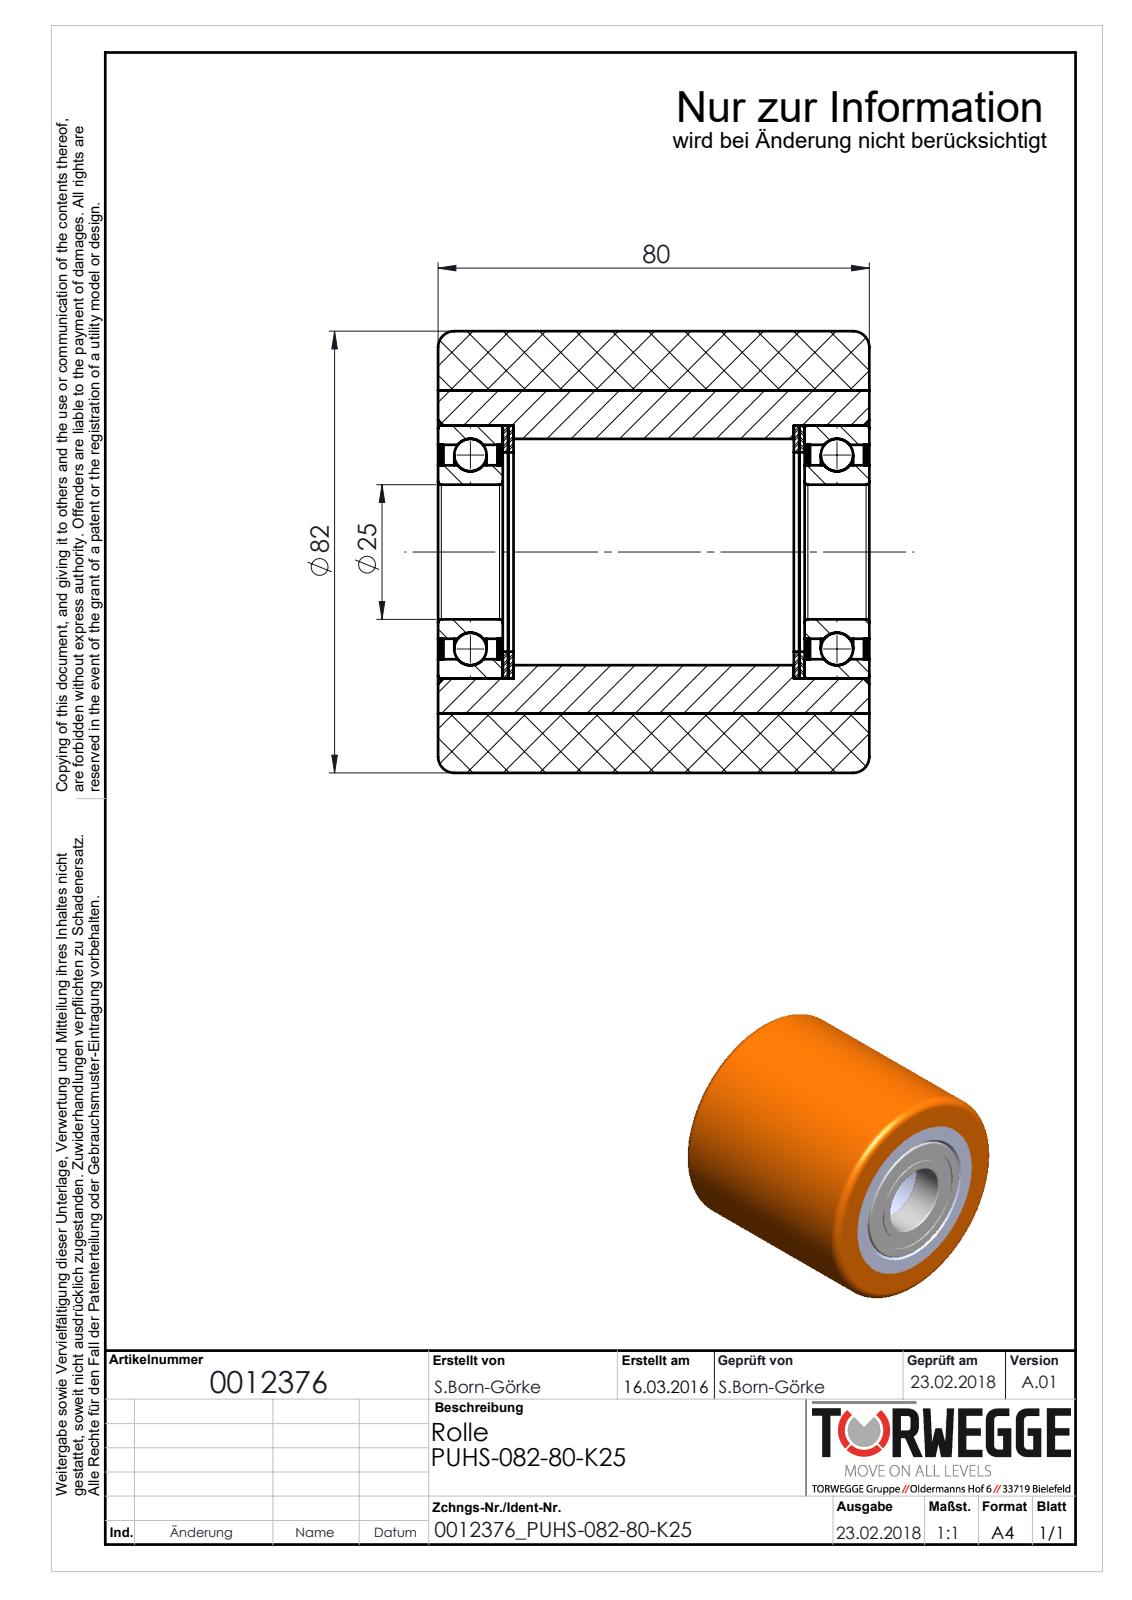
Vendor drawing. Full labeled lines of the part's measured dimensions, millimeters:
Part name (STEP PRODUCT): 0012376_PUHS-082-80-K25
STEP written by: SolidWorks 2016 (AUTOMOTIVE_DESIGN)
Units: millimetres
Bodies: 16 solids, 158 faces (30 planar, 68 cylindrical, 60 other)
Overall size (bounding box): 82 × 82 × 80
Volume: 328 220 mm³ · Surface area: 97 283 mm²
Round holes (diameter × count): ⌀25 ×1, ⌀32.2 ×1, ⌀37 ×1, ⌀39.8 ×1, ⌀42 ×1, ⌀60 ×1
Round bosses / shafts (diameter × count): ⌀82 ×1, ⌀47 ×1
Main face-to-face distances: 1, 68, 12, 0.5, 13, 67, 55, 80, 54, 66
